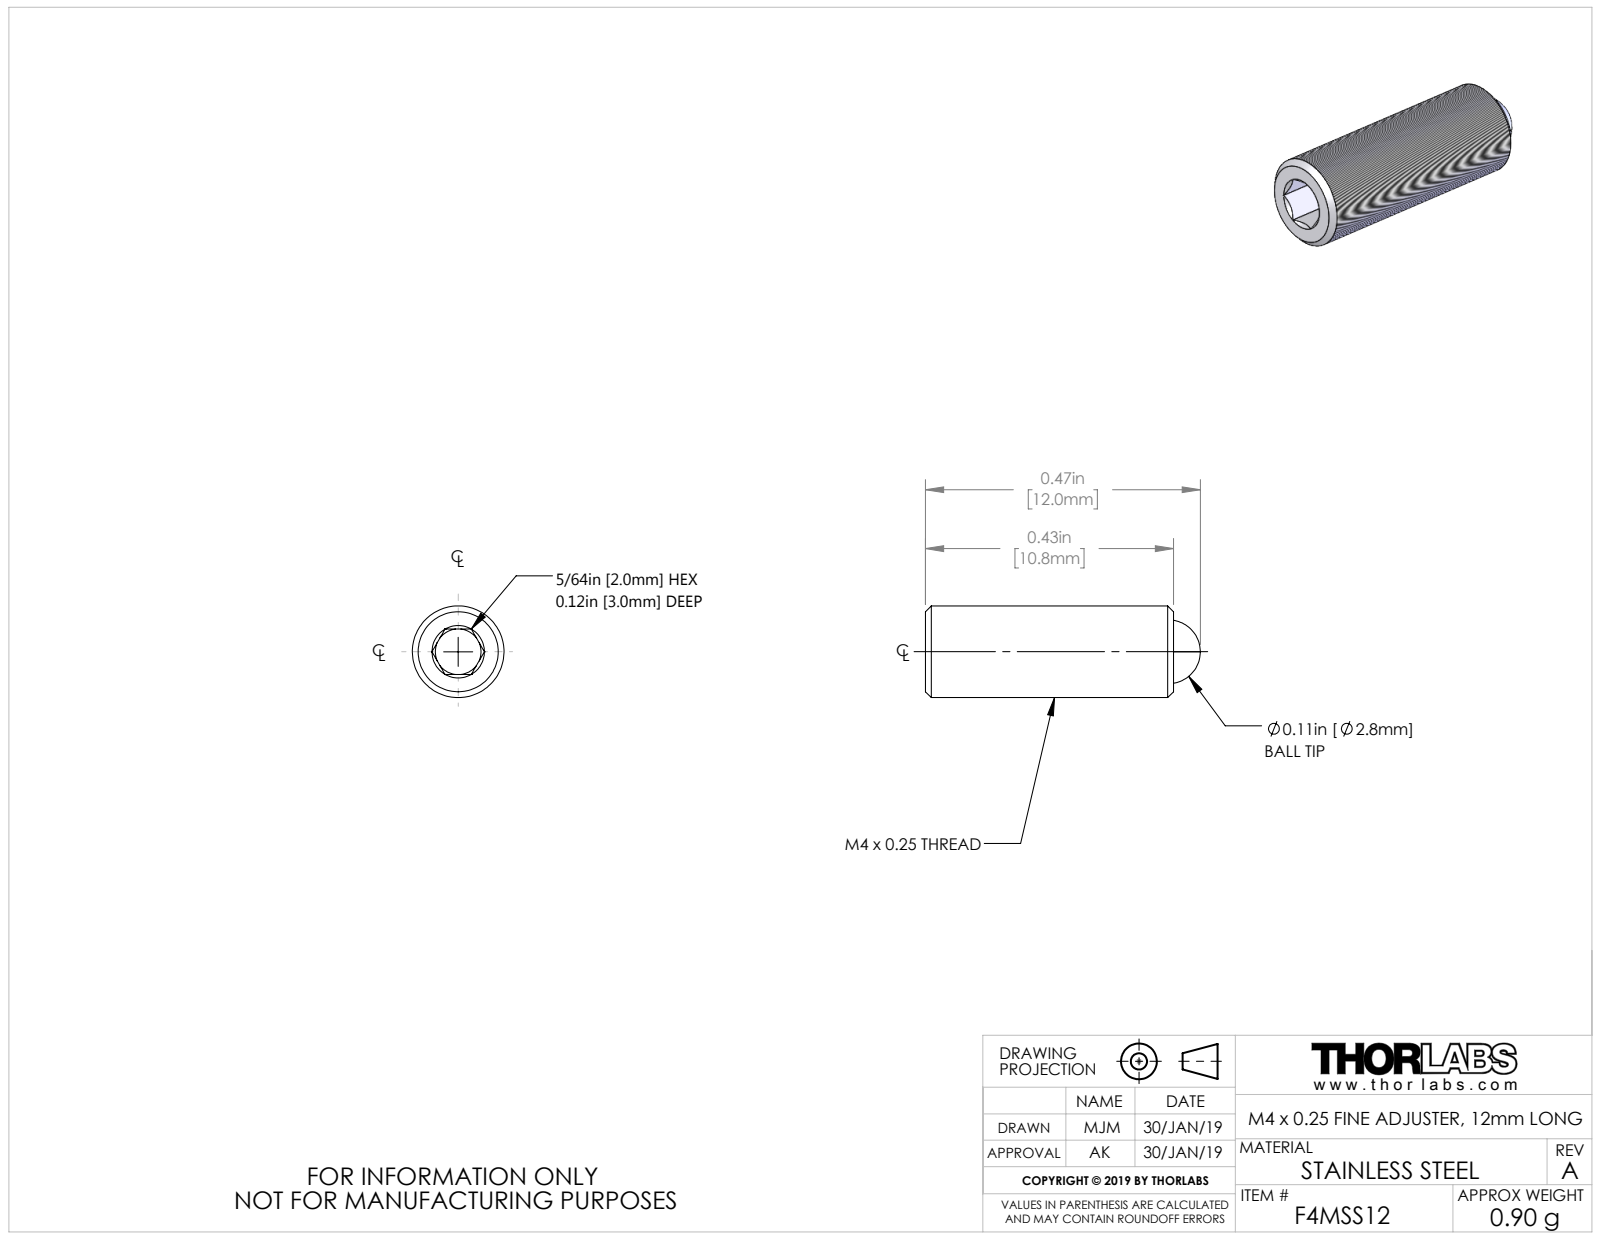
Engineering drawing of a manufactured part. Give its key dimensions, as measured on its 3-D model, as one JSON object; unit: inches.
{"part_name": "TTN174698-E0W", "step_written_by": "SolidWorks 2018 (AUTOMOTIVE_DESIGN)", "units": "inches", "bodies": {"solids": 2, "faces": 45, "planar": 20, "cylindrical": 6, "other": 19}, "overall_size": [0.472, 0.157, 0.157], "volume_in3": 0.008, "surface_area_in2": 0.338, "round_holes": [[0.079, 1], [0.11, 1]], "round_bosses_or_shafts": [[0.157, 1]], "face_to_face_distances": [0.078, 0.426, 0.078, 0.306, 0.12]}
